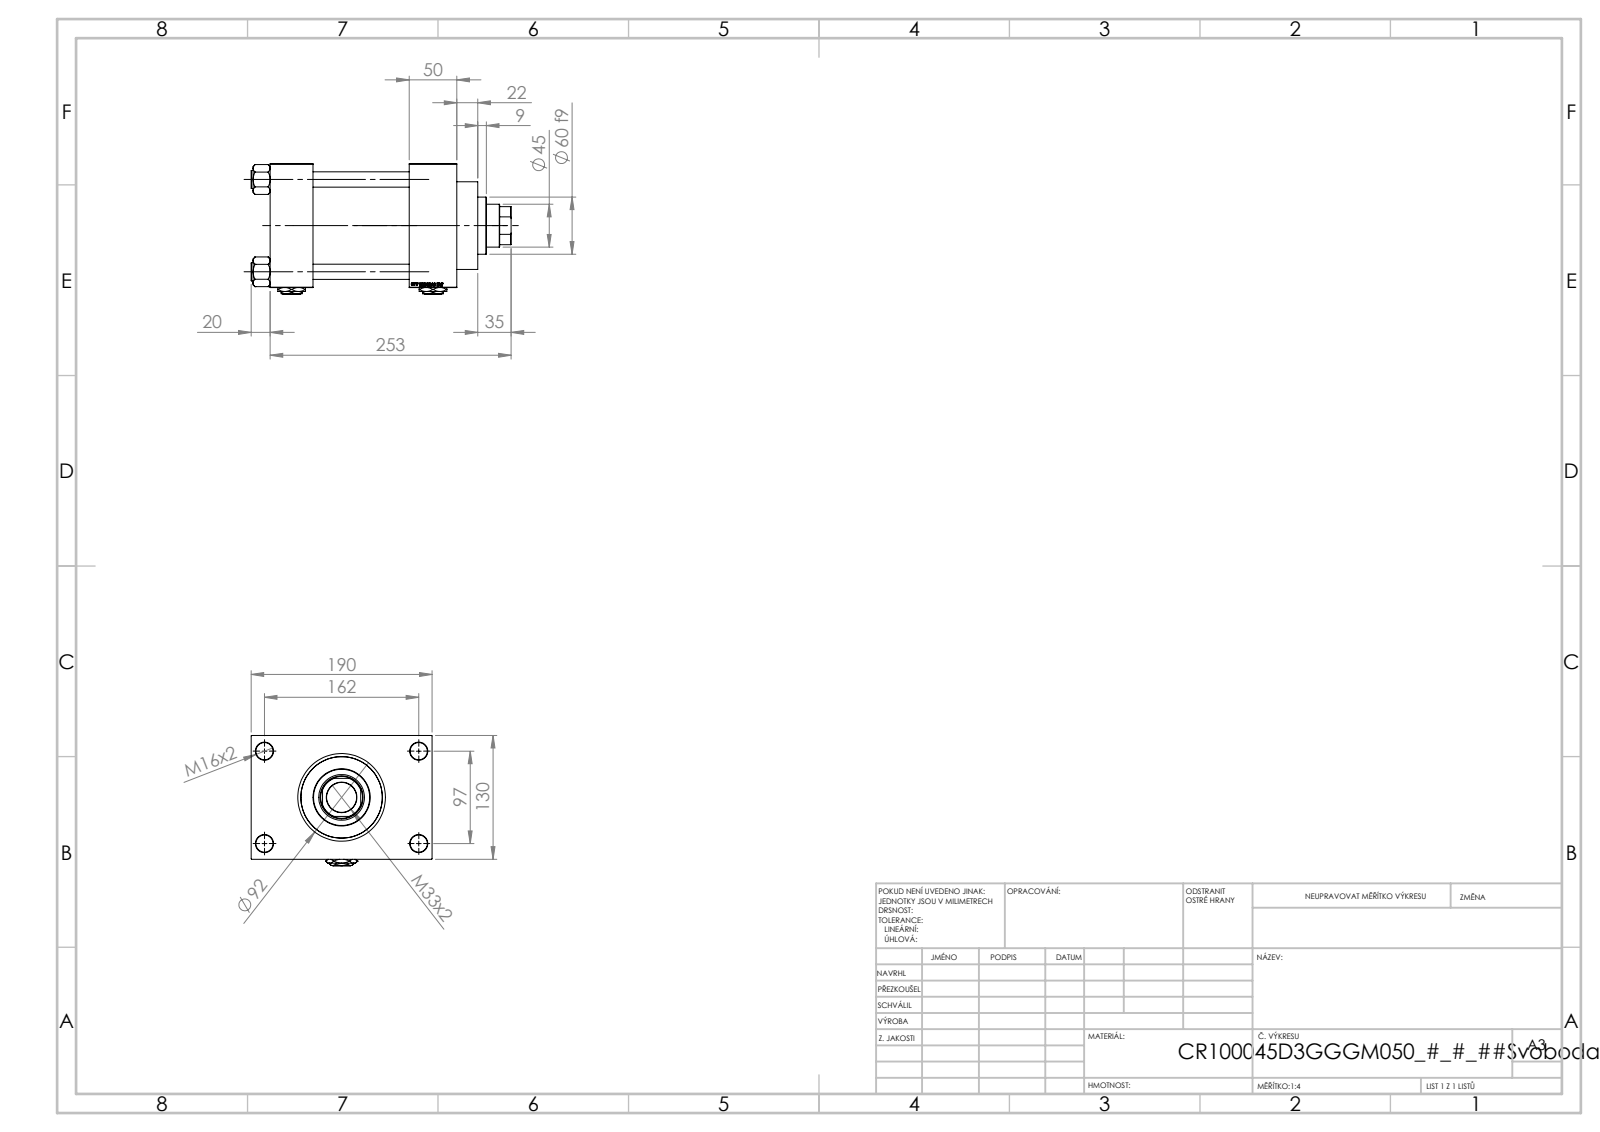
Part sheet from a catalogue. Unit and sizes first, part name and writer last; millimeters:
Units: millimetres
Overall size (bounding box): 273 × 190 × 137
Round holes (diameter × count): ⌀16 ×4, ⌀18 ×4, ⌀7 ×2, ⌀26.44 ×2, ⌀35 ×2, ⌀31.5 ×1, ⌀45 ×1, ⌀48 ×1, ⌀76 ×1, ⌀85.5 ×1, ⌀100 ×1
Round bosses / shafts (diameter × count): ⌀19 ×4, ⌀106 ×1, ⌀92 ×1, ⌀60 ×1
Partial cylindrical surfaces — rounded edges, fillets, slot ends (radius × count): R22 ×1
Main face-to-face distances: 50, 130, 45, 146, 101, 196, 151, 30, 160, 190
Hole centre spacings: 32.55, 68.52, 94.41, 96.9, 102.27, 129.45, 161.73, 97
Volume: 2 693 000 mm³ · Surface area: 389 000 mm²
Bodies: 13 solids, 1253 faces (593 planar, 100 cylindrical, 560 other)
Part name (STEP PRODUCT): NUT_M5_D; Zatka_pro_OIL_PORT; V215CR_D_TYCINKA; V215_VC_A (+2 more)
STEP written by: SolidWorks 2019 (CONFIG_CONTROL_DESIGN)
